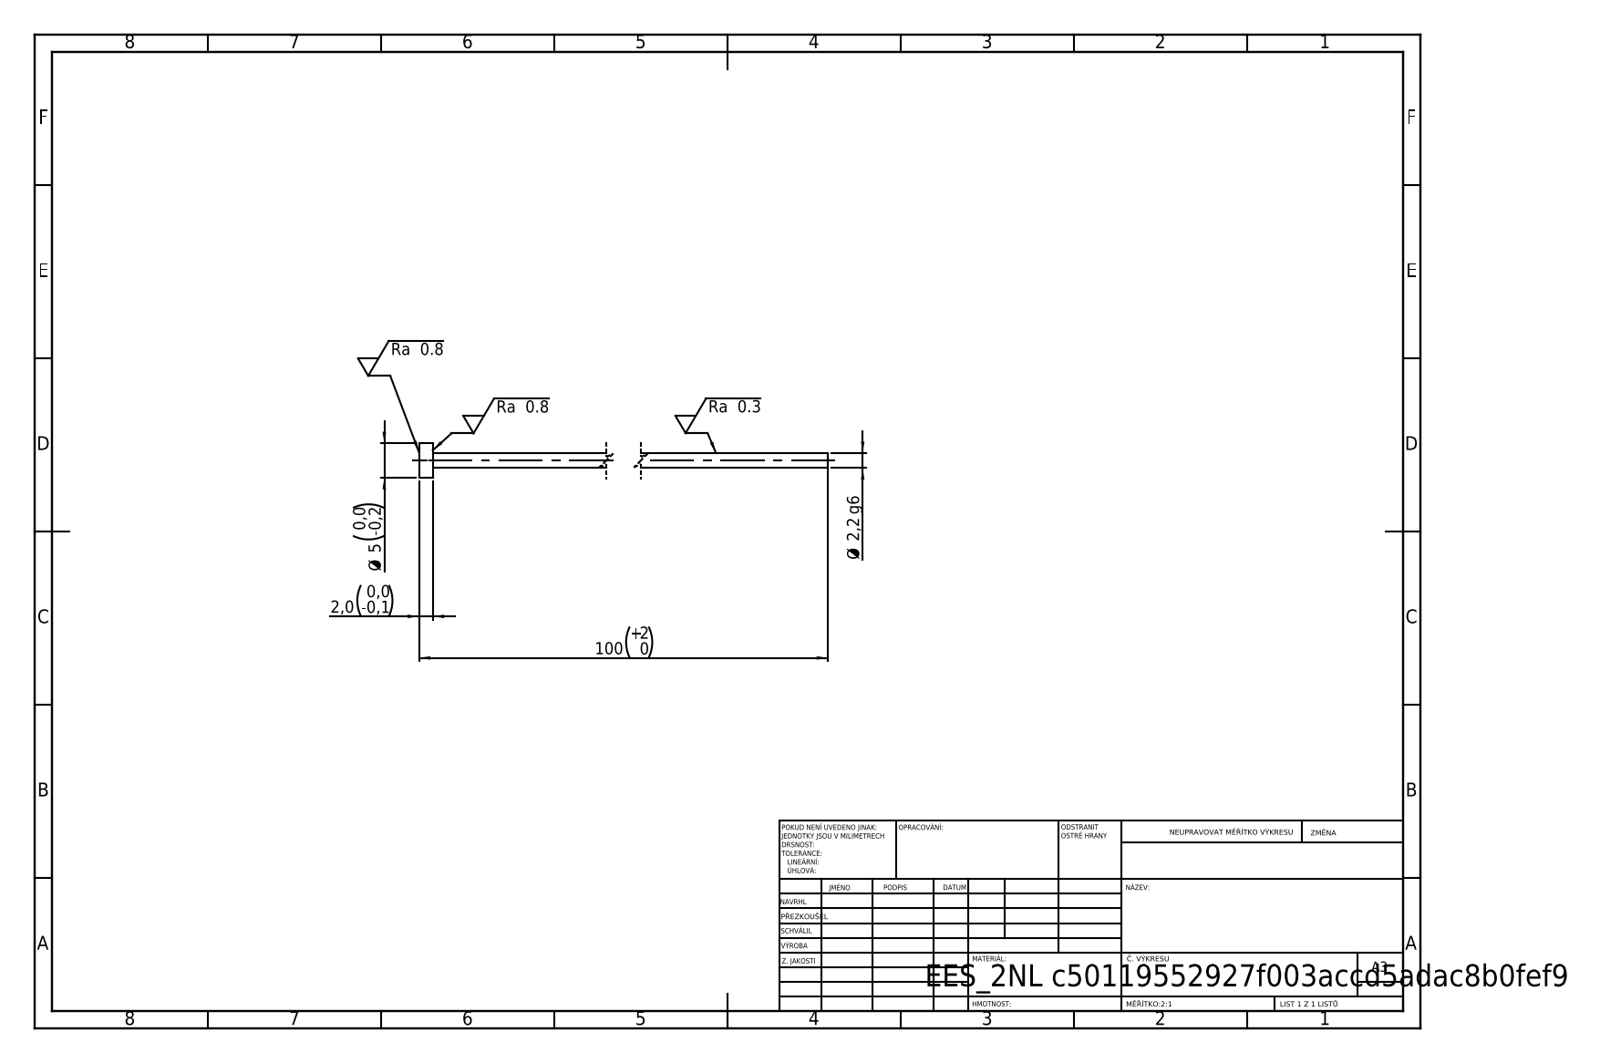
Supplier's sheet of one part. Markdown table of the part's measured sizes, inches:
| quantity | value |
| --- | --- |
| STEP written by | SolidWorks 2019 (CONFIG_CONTROL_DESIGN) |
| units | inches |
| bodies | 1 solid, 7 faces (3 planar, 4 cylindrical, 0 other) |
| overall size | 3.937 × 0.197 × 0.197 |
| volume | 0.025 in³ |
| surface area | 1.16 in² |
| round bosses / shafts (diameter × count) | 0.197 × 1, 0.087 × 1 |
| main face-to-face distances | 0.079, 3.937, 3.858 |
